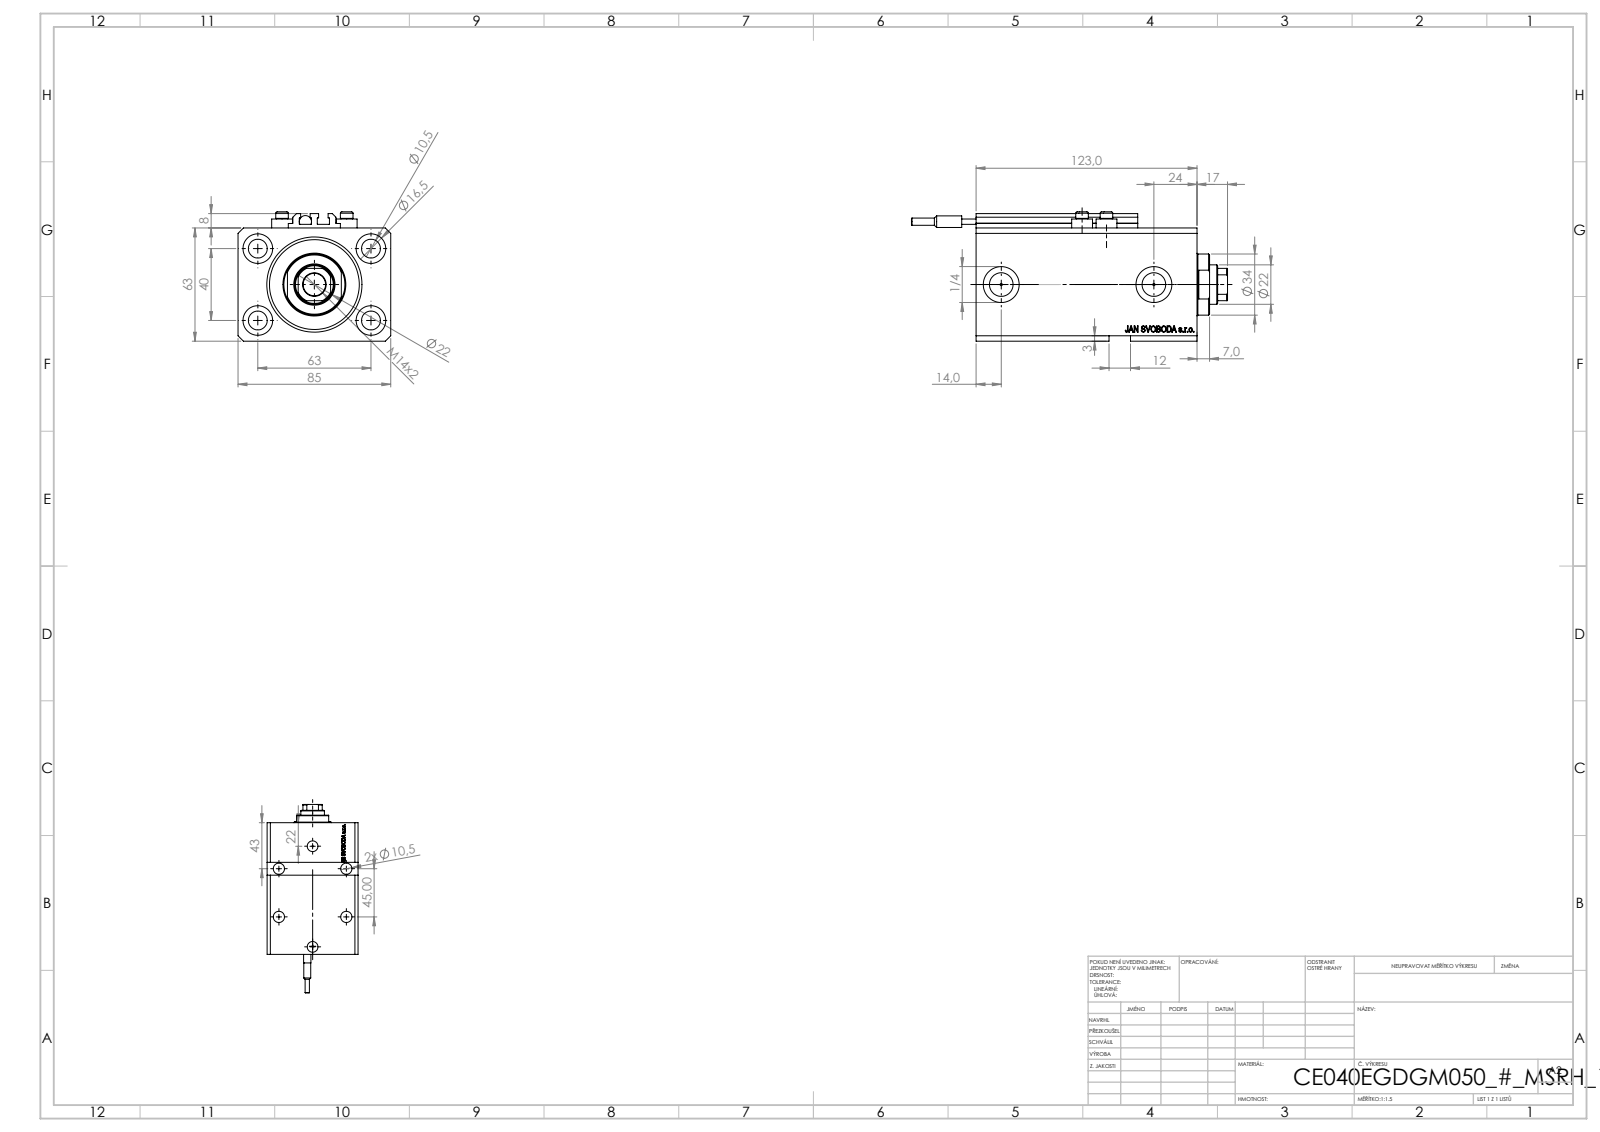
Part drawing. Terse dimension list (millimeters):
name: V250CE_C_VCP; SWITCH_V250CE; ALLEN BOLT V250CE; V250CE_VC_E (+1 more)
written by: SolidWorks 2019 (CONFIG_CONTROL_DESIGN)
unit: mm
bodies: 9 solids, 1149 faces (555 planar, 164 cylindrical, 430 other)
size: 176 × 85 × 72
volume: 554 803 mm³; area: 121 859 mm²
holes: 8× ⌀10.5, 4× ⌀1.25, 4× ⌀4, 4× ⌀16.5, 2× ⌀10, 2× ⌀13.16, 2× ⌀20, 1× ⌀12.5, 1× ⌀22, 1× ⌀40, 1× ⌀53
bosses: 4× ⌀11.6, 4× ⌀7, 1× ⌀34, 1× ⌀6.8, 1× ⌀6.5, 1× ⌀4
rounds: 10× R0.2, 1× R10.5
face distances: 63, 85, 123, 17, 106, 11.4, 94.6, 111.6, 3, 65
hole spacings: 37.31, 63, 13.6, 15.4, 24.96, 27.54, 33.62, 36
